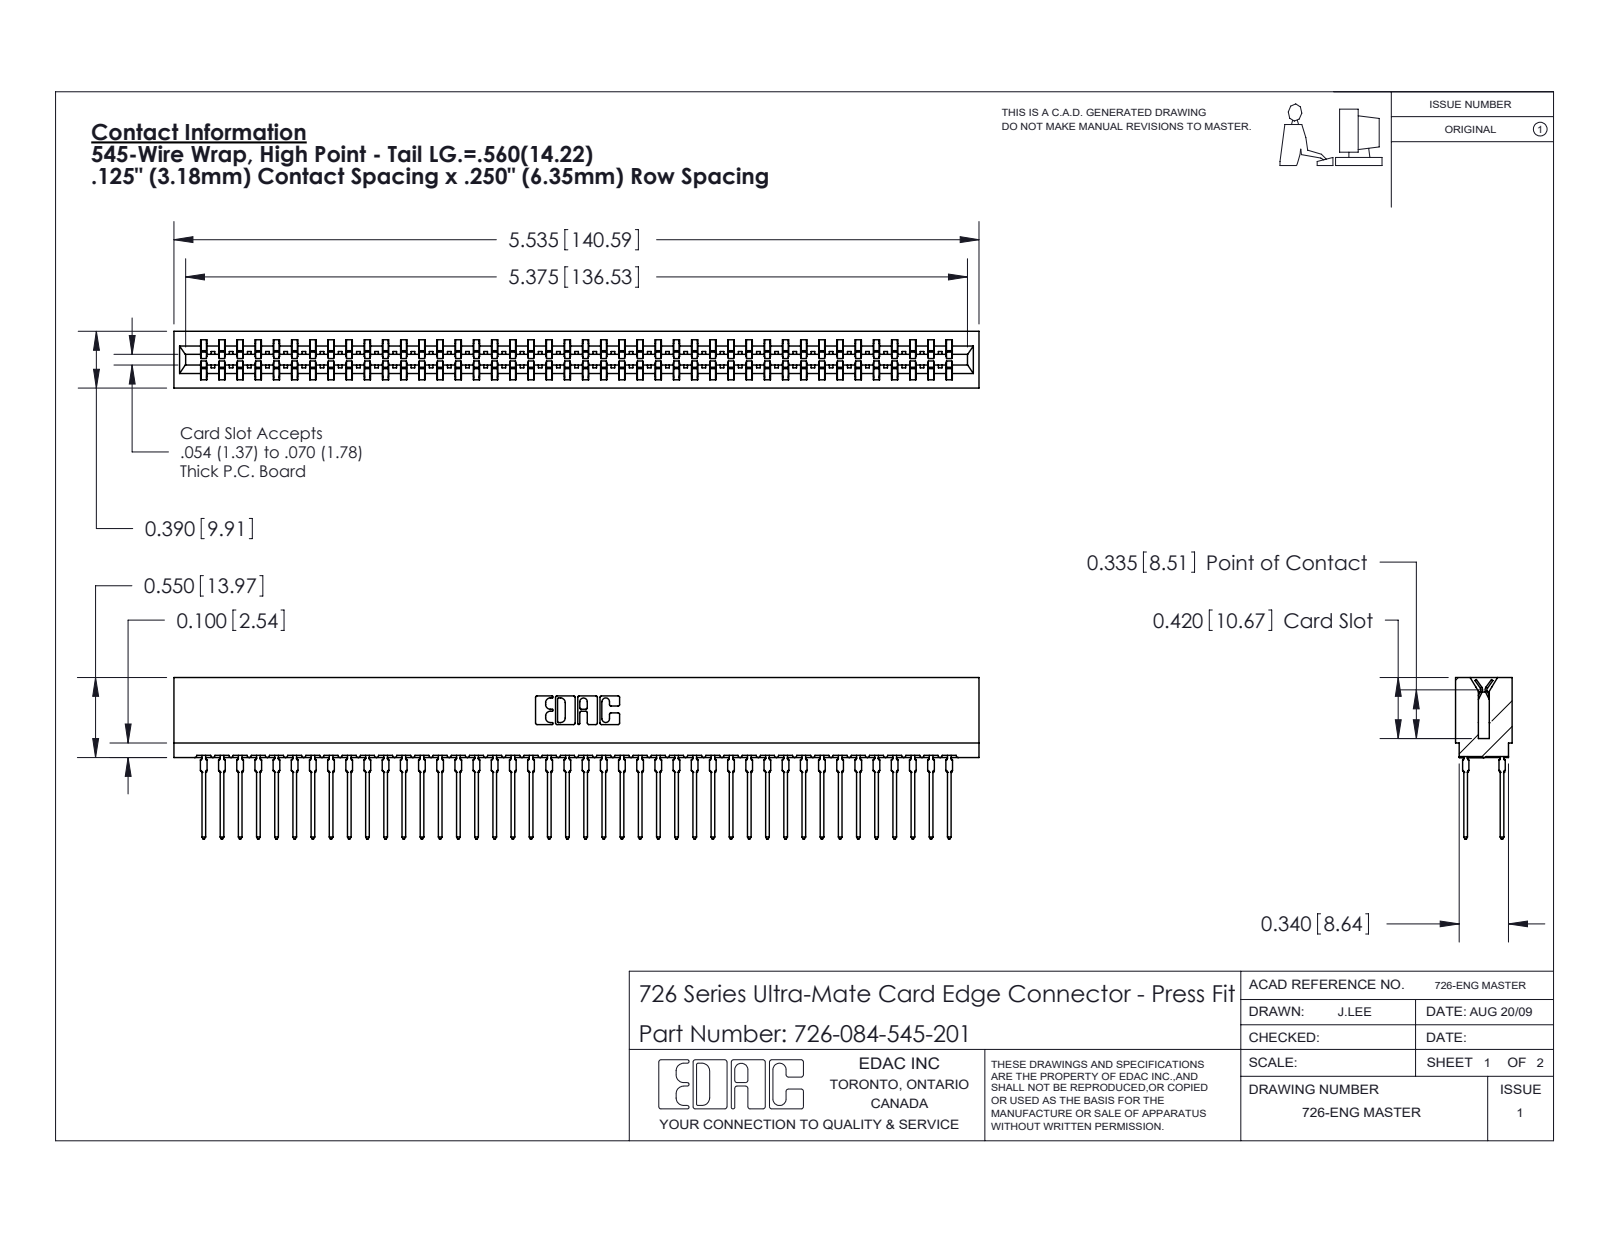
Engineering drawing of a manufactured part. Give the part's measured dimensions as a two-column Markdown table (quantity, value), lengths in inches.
| quantity | value |
| --- | --- |
| part name | 726-084-545-201; 746-292-001_545; 726 Part_.515 Slot Depth - 01 |
| STEP written by | SolidWorks 2020 (CONFIG_CONTROL_DESIGN) |
| units | inches |
| bodies | 85 solids, 7615 faces (3919 planar, 1512 cylindrical, 2184 other) |
| overall size | 5.535 × 1.109 × 0.39 |
| volume | 0.807 in³ |
| surface area | 36.25 in² |
| partial cylindrical surfaces (radius × count) | 0.021 × 168, 0.015 × 43, 0.01 × 22, 0.005 × 8, 0.011 × 8, 0.007 × 6, 0.031 × 6, 0.026 × 3 |
| main face-to-face distances | 0.057, 0.333, 0.025, 0.307, 0.25, 0.39, 0.083, 0.275, 0.5, 0.365 |
